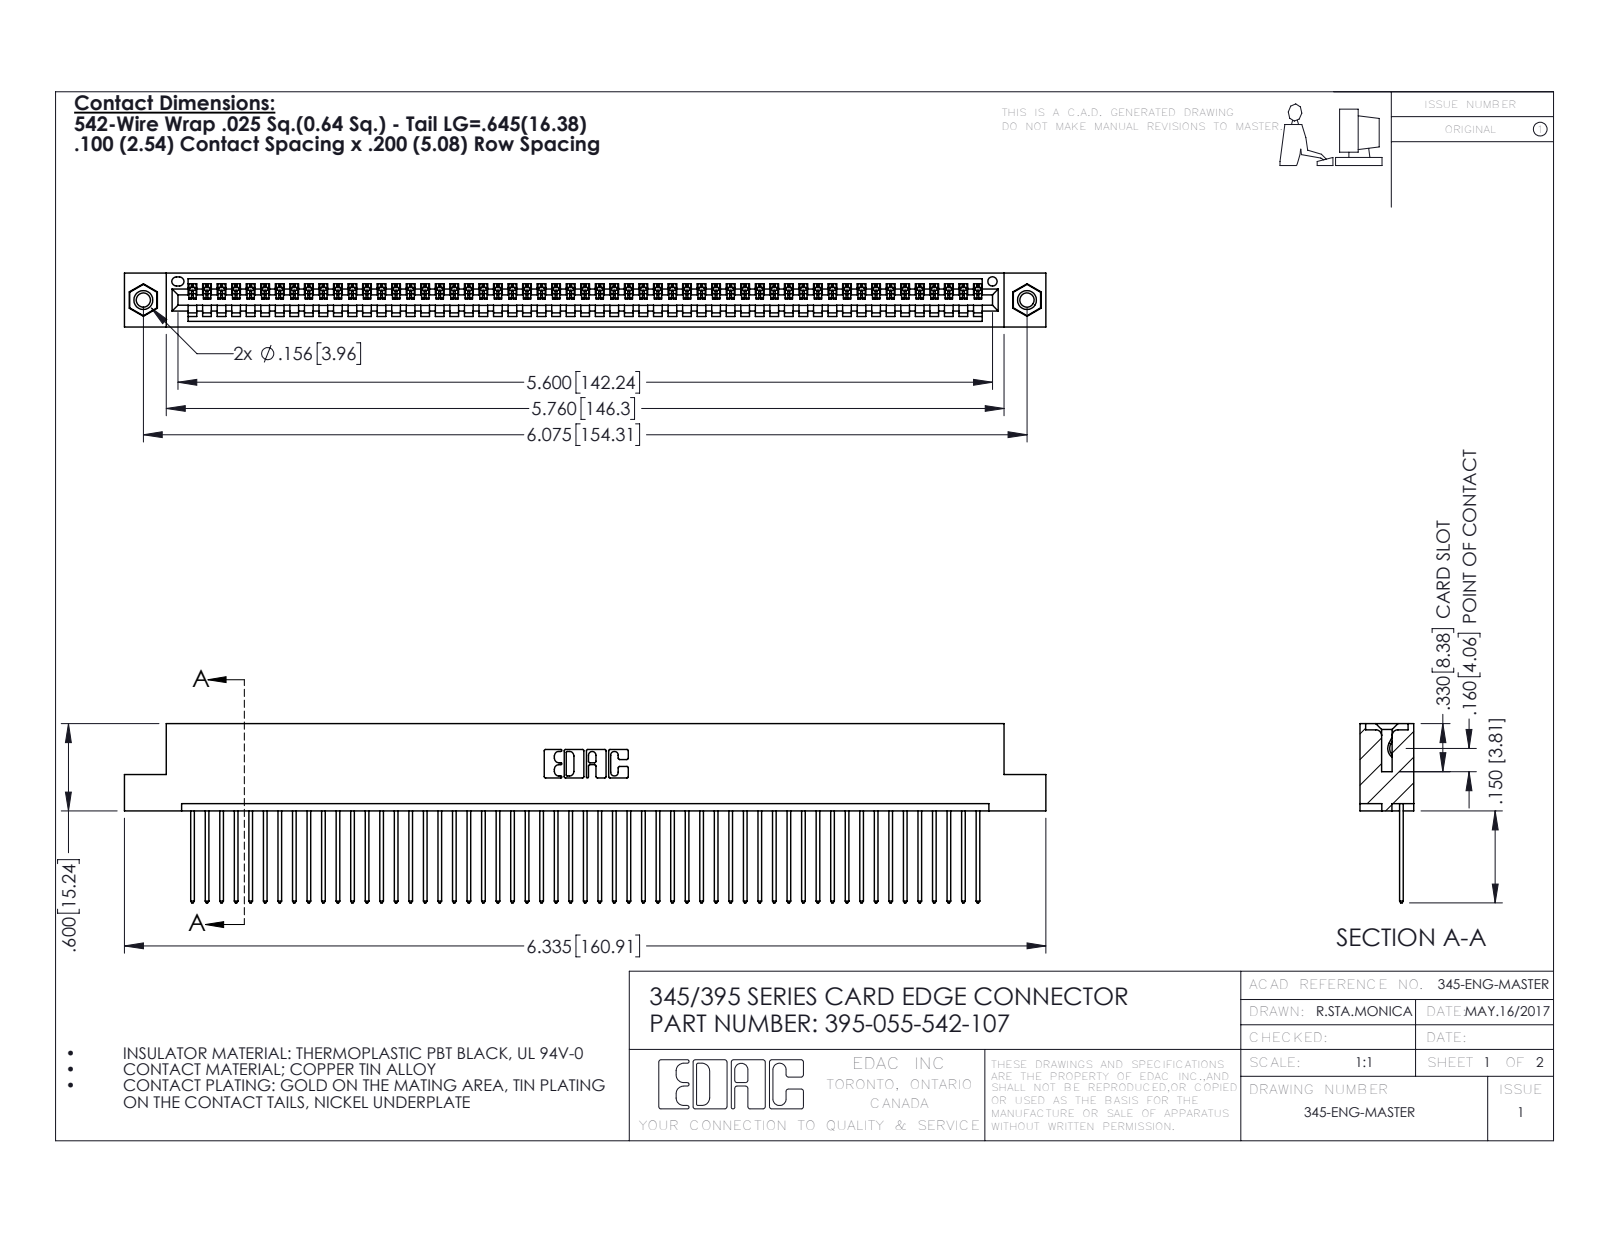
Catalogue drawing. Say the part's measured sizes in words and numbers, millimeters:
The part is named "345-250-001_345-250-005-103; 395-055-542-107; 345 Part_Flush Mounting Lugs - 0.156 Dia-TI; 345-292-001_345-293-142". Its 3-D file was written by "SolidWorks 2016 (CONFIG_CONTROL_DESIGN)". It is 58 solids with 3376 faces: 2312 planar, 1048 cylindrical and 16 other. Overall it measures 160.9 by 31.3 by 9.4 millimeters. Its volume is 15 500 cubic millimeters and its surface area 21 580 square millimeters. Round holes: 2 of diameter 2.5, 2 of diameter 3.2, 2 of diameter 4, 1 of diameter 1.6. Round bosses or shafts: 2 of diameter 3.9. Partial cylindrical surfaces (rounded edges, fillets, slot ends): 110 of radius 0.2, 110 of radius 0.3, 22 of radius 0.3, 6 of radius 0.2, 6 of radius 0.8, 3 of radius 0.7, 2 of radius 0.8, 2 of radius 1. The main face-to-face distances are 1.8, 7.6, 2.5, 6.9, 0.6, 9.4, 5.1, 5.7, 3.8, 1.8. The hole center spacings are 6.9, 148.3, 154.3.
